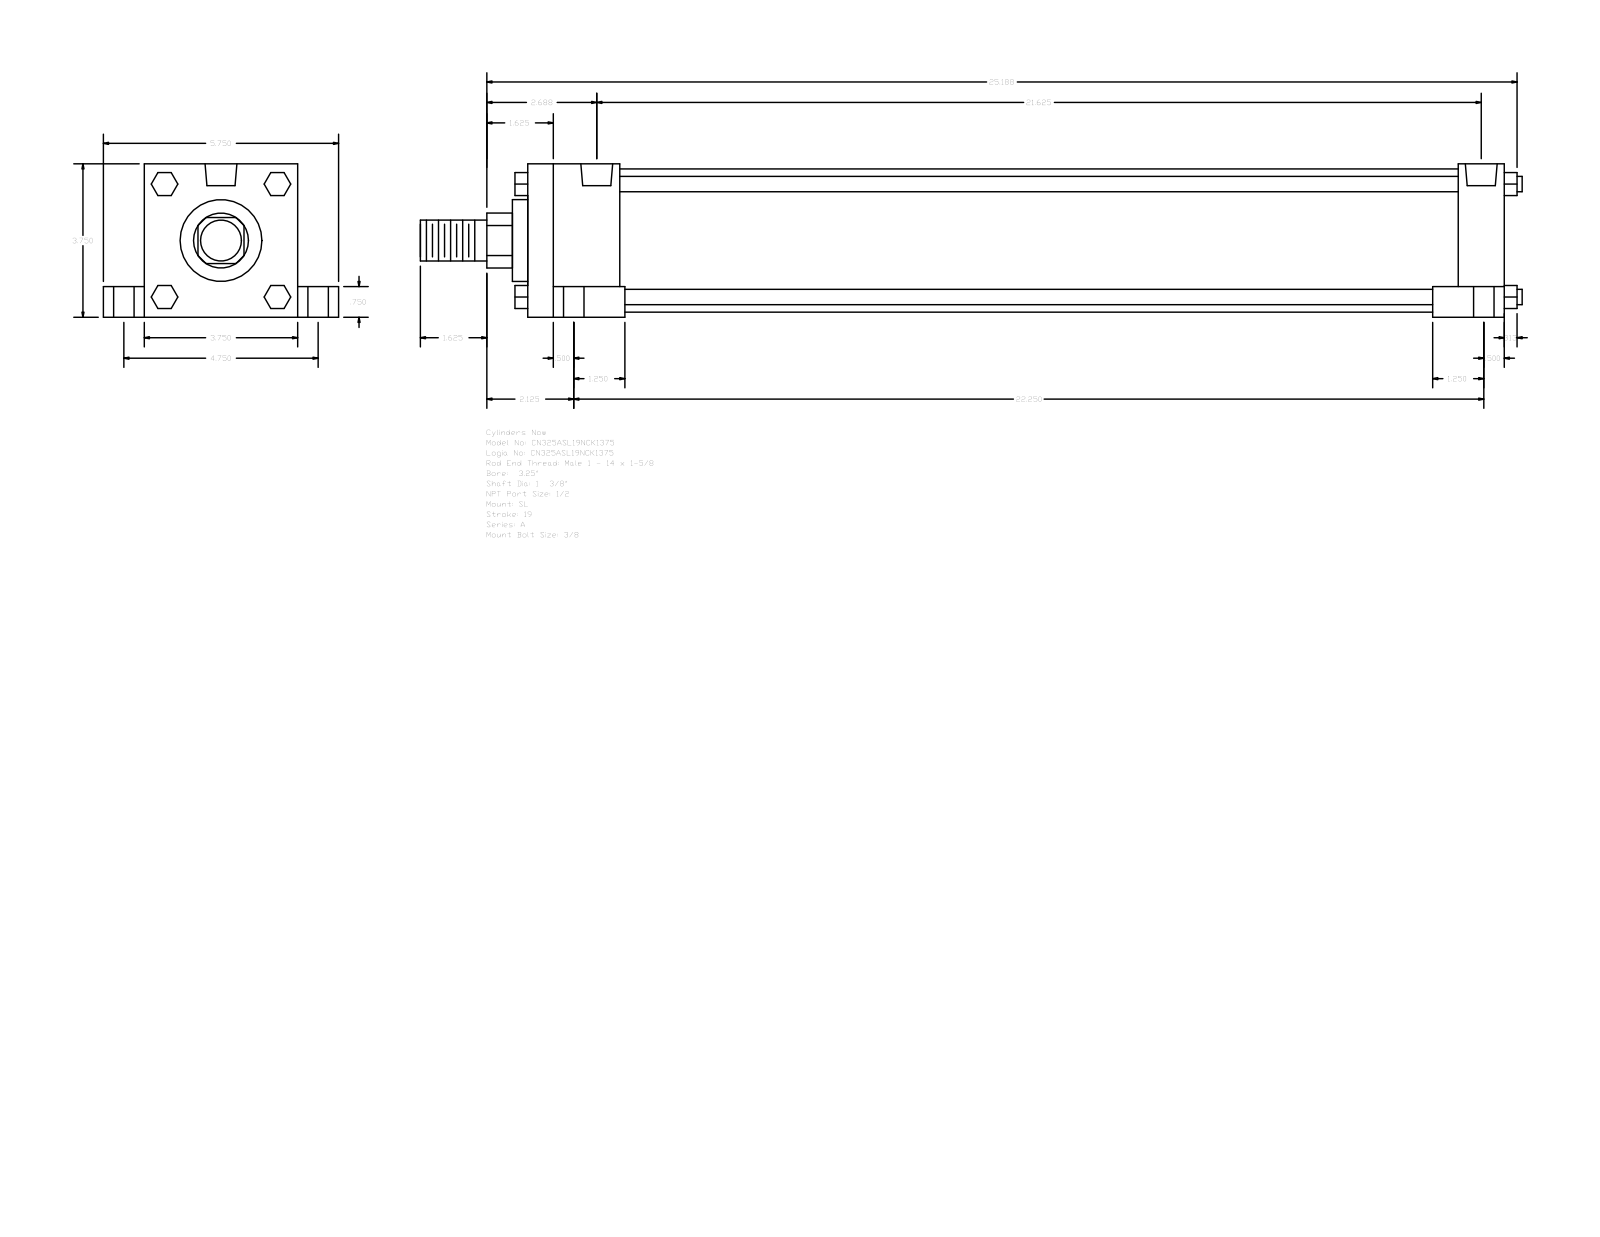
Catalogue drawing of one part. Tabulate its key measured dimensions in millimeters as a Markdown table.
| quantity | value |
| --- | --- |
| part name | A_SL__0325_1.375 |
| STEP written by | GSSL Pune (CONFIG_CONTROL_DESIGN) |
| units | millimeters |
| bodies | 0 solids, 150 faces (114 planar, 36 cylindrical, 0 other) |
| overall size | 684.21 × 146.05 × 95.25 |
| round holes (diameter × count) | 8.73 × 4, 12.7 × 4, 19.05 × 4, 19.77 × 2 |
| round bosses / shafts (diameter × count) | 9.53 × 4, 88.9 × 1, 50.8 × 1, 34.92 × 1, 25.4 × 1 |
| partial cylindrical surfaces (radius × count) | 17.06 × 1 |
| main face-to-face distances | 95.24, 606.43, 25.41, 120.65, 19.05, 76.19, 57.15, 28.58, 577.85, 520.7 |
| hole center spacings | 3.18, 60.35, 60.52, 62, 62.81, 120.66, 542.92, 546.1 |
